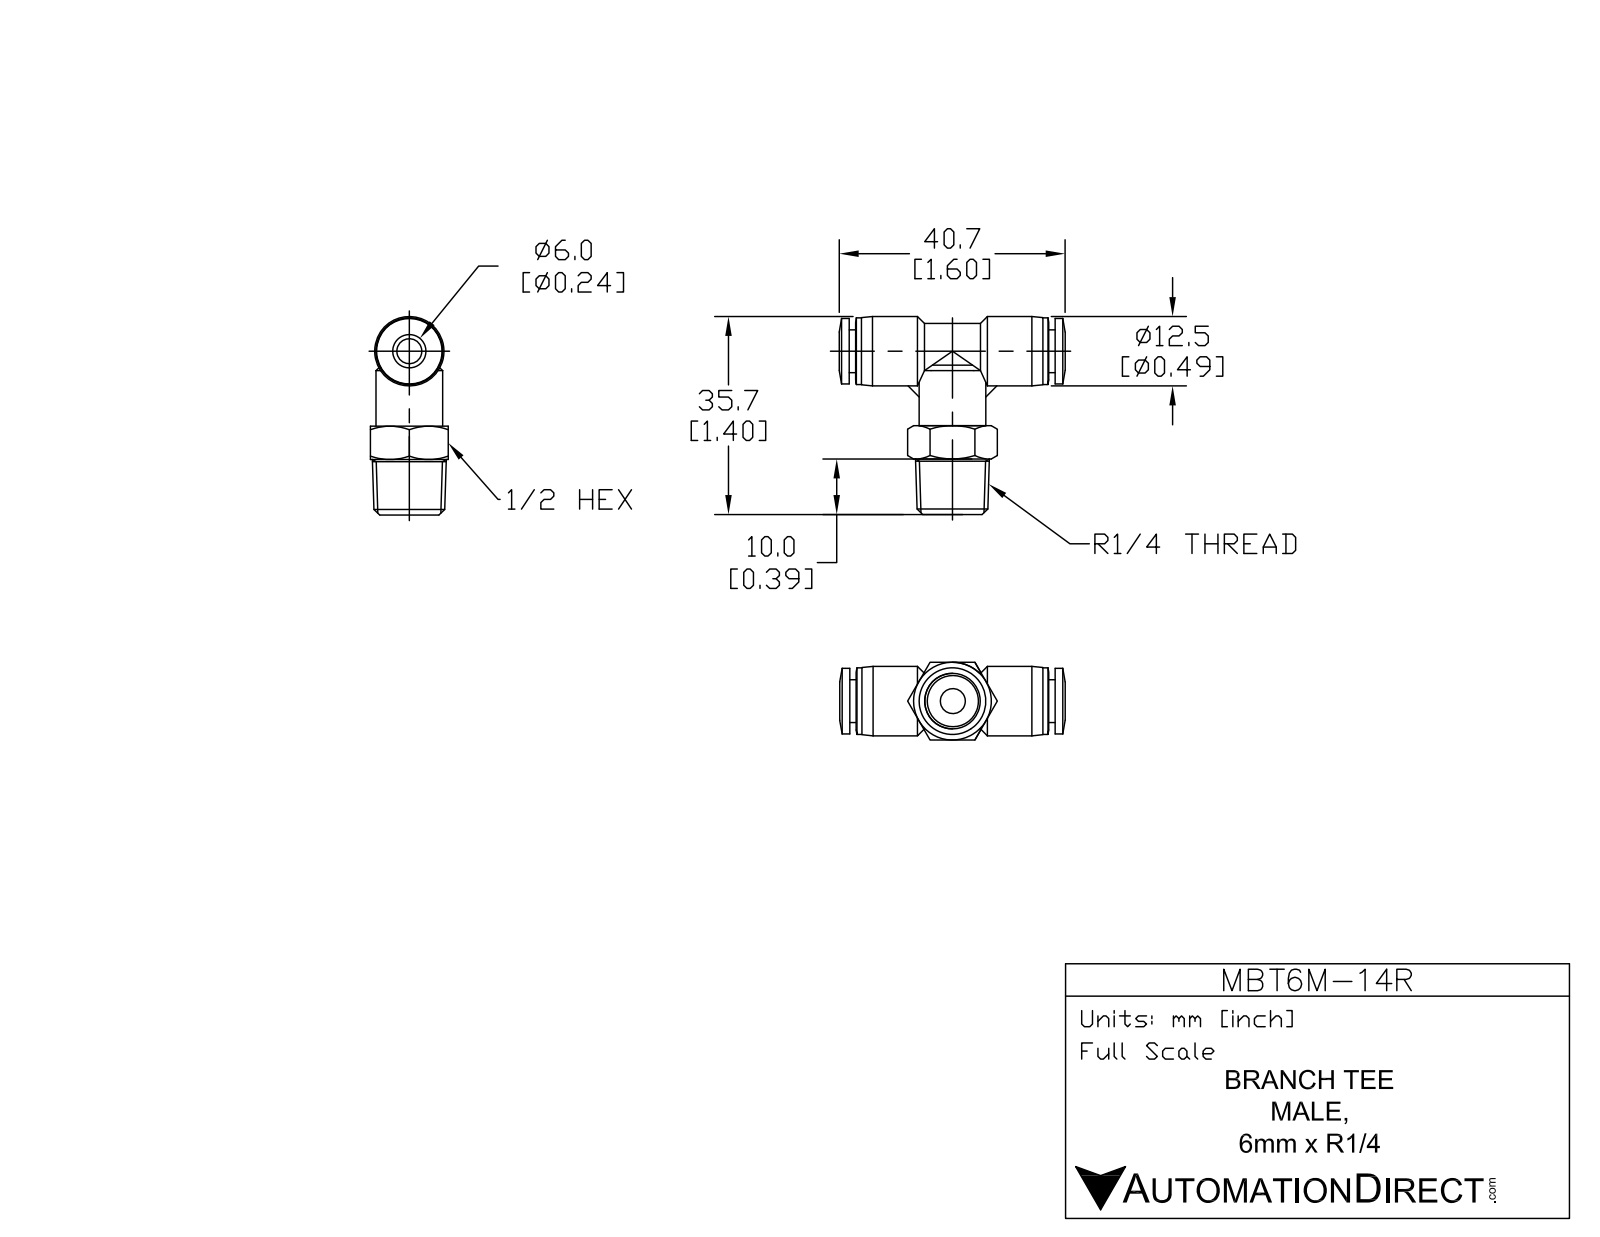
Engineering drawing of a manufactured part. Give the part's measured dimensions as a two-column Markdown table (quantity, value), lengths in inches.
| quantity | value |
| --- | --- |
| part name | MBT6M-14R |
| STEP written by | SolidWorks 2015 (AUTOMOTIVE_DESIGN) |
| units | inches |
| bodies | 1 solid, 96 faces (25 planar, 31 cylindrical, 40 other) |
| overall size | 1.598 × 1.407 × 0.551 |
| volume | 0.37 in³ |
| surface area | 6.39 in² |
| round holes (diameter × count) | 0.157 × 2, 0.248 × 1 |
| round bosses / shafts (diameter × count) | 0.472 × 2, 0.492 × 1, 0.465 × 1, 0.303 × 1 |
| partial cylindrical surfaces (radius × count) | 0.187 × 2 |
| main face-to-face distances | 0.551, 0.045, 1.411, 1.457, 0.63, 1.366, 0.575, 0.882, 0.53, 0.837 |
